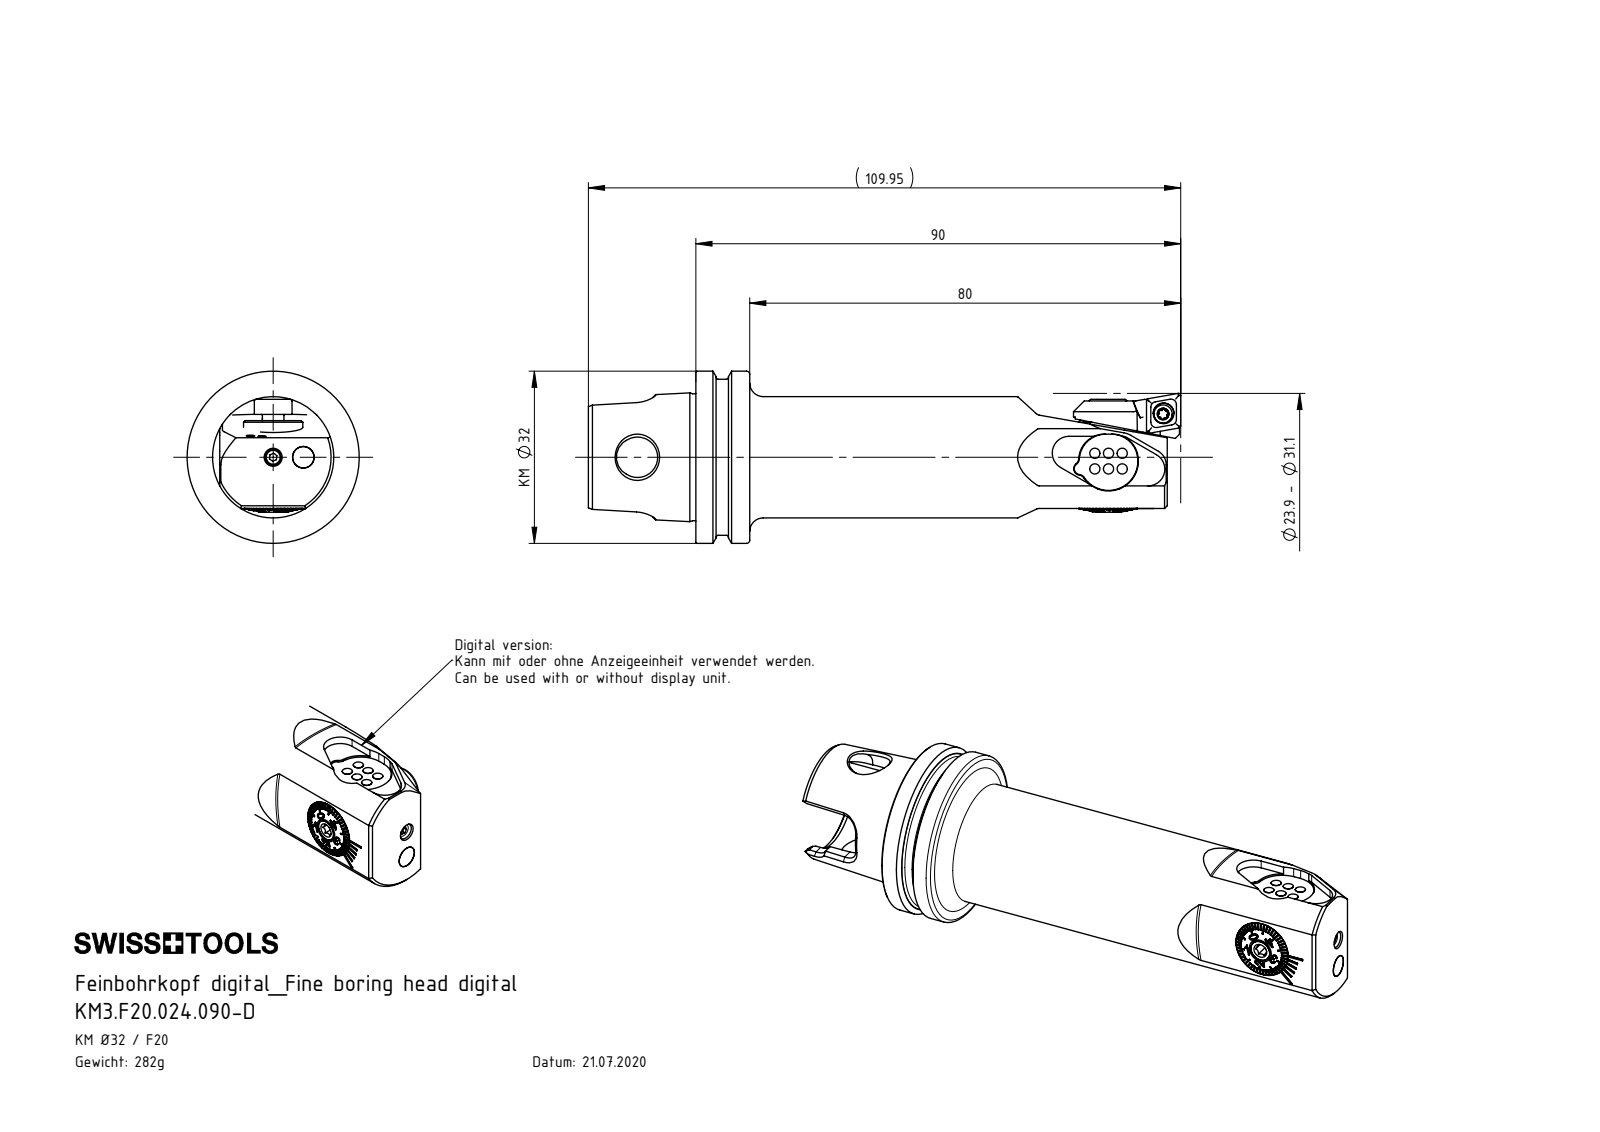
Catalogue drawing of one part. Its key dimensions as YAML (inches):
part_name: "F20-BG2.007.006_A; DIN 3771 - 11x1_x; KM3-F20.DA3.090_B_bohrungen gefüllt; KM3.F20.024.090-D (+8 more)"
step_written_by: "SolidWorks 2022 (CONFIG_CONTROL_DESIGN)"
units: inches
bodies: {solids: 14, faces: 866, planar: 410, cylindrical: 159, other: 297}
overall_size: [4.23, 1.258, 1.258]
volume: 2.216
surface_area: 22.94
round_holes:
  - {diameter: 0.083, count: 4}
  - {diameter: 0.059, count: 2}
  - {diameter: 0.118, count: 2}
  - {diameter: 0.13, count: 2}
  - {diameter: 0.043, count: 1}
  - {diameter: 0.075, count: 1}
  - {diameter: 0.157, count: 1}
  - {diameter: 0.165, count: 1}
  - {diameter: 0.177, count: 1}
  - {diameter: 0.226, count: 1}
  - {diameter: 0.236, count: 1}
  - {diameter: 0.244, count: 1}
round_bosses_or_shafts:
  - {diameter: 0.075, count: 6}
  - {diameter: 0.157, count: 2}
  - {diameter: 0.156, count: 2}
  - {diameter: 1.258, count: 1}
  - {diameter: 1.14, count: 1}
  - {diameter: 0.886, count: 1}
  - {diameter: 0.433, count: 1}
  - {diameter: 0.432, count: 1}
partial_cylinders:
  - {radius: 0.043, count: 3}
  - {radius: 0.047, count: 3}
  - {radius: 0.118, count: 3}
  - {radius: 0.012, count: 2}
  - {radius: 0.049, count: 2}
  - {radius: 0.079, count: 2}
  - {radius: 0.122, count: 2}
  - {radius: 0.139, count: 2}
face_to_face_distances: [3.445, 0.394, 3.051, 0.02, 0.098, 0.374, 3.425, 0.146, 0.059, 0.079]
hole_center_spacings: [0.039, 0.212, 0.22, 0.343]
